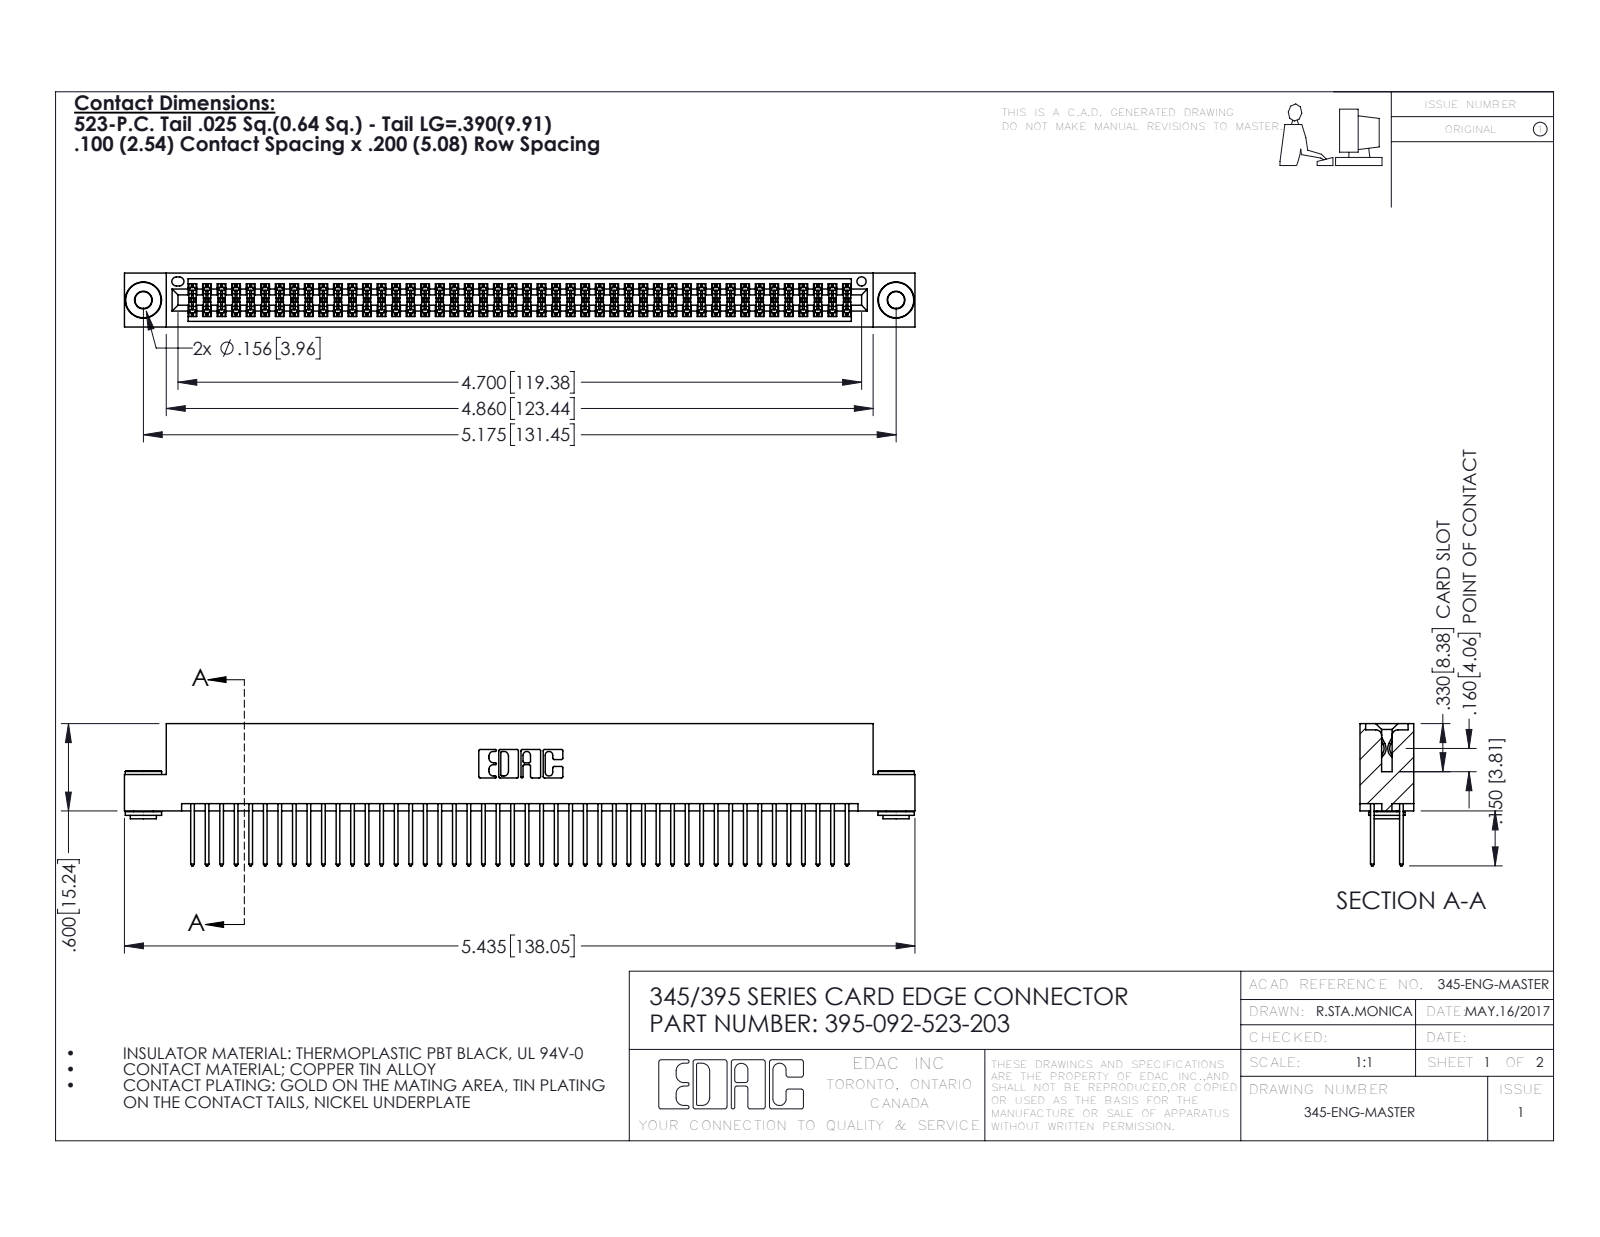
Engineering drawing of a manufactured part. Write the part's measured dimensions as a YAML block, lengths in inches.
part_name: "345-250-002_345-250-002-102; 345 Part_Flush Mounting Lugs - 0.156 Dia-TH; 395-092-523-203; 345-292-001_345-293-123"
step_written_by: "SolidWorks 2016 (CONFIG_CONTROL_DESIGN)"
units: inches
bodies: {solids: 95, faces: 4764, planar: 3126, cylindrical: 1630, other: 8}
overall_size: [5.435, 0.977, 0.37]
volume: 0.833
surface_area: 33.04
round_holes:
  - {diameter: 0.116, count: 2}
  - {diameter: 0.156, count: 2}
  - {diameter: 0.064, count: 1}
round_bosses_or_shafts:
  - {diameter: 0.25, count: 2}
  - {diameter: 0.18, count: 2}
  - {diameter: 0.136, count: 2}
partial_cylinders:
  - {radius: 0.006, count: 138}
  - {radius: 0.01, count: 92}
  - {radius: 0.01, count: 22}
  - {radius: 0.007, count: 6}
  - {radius: 0.031, count: 6}
  - {radius: 0.026, count: 3}
  - {radius: 0.014, count: 2}
  - {radius: 0.019, count: 2}
face_to_face_distances: [0.072, 0.298, 0.2, 0.025, 0.098, 0.272, 0.37, 0.225, 0.175, 0.149]
hole_center_spacings: [0.27, 4.939, 5.175]
